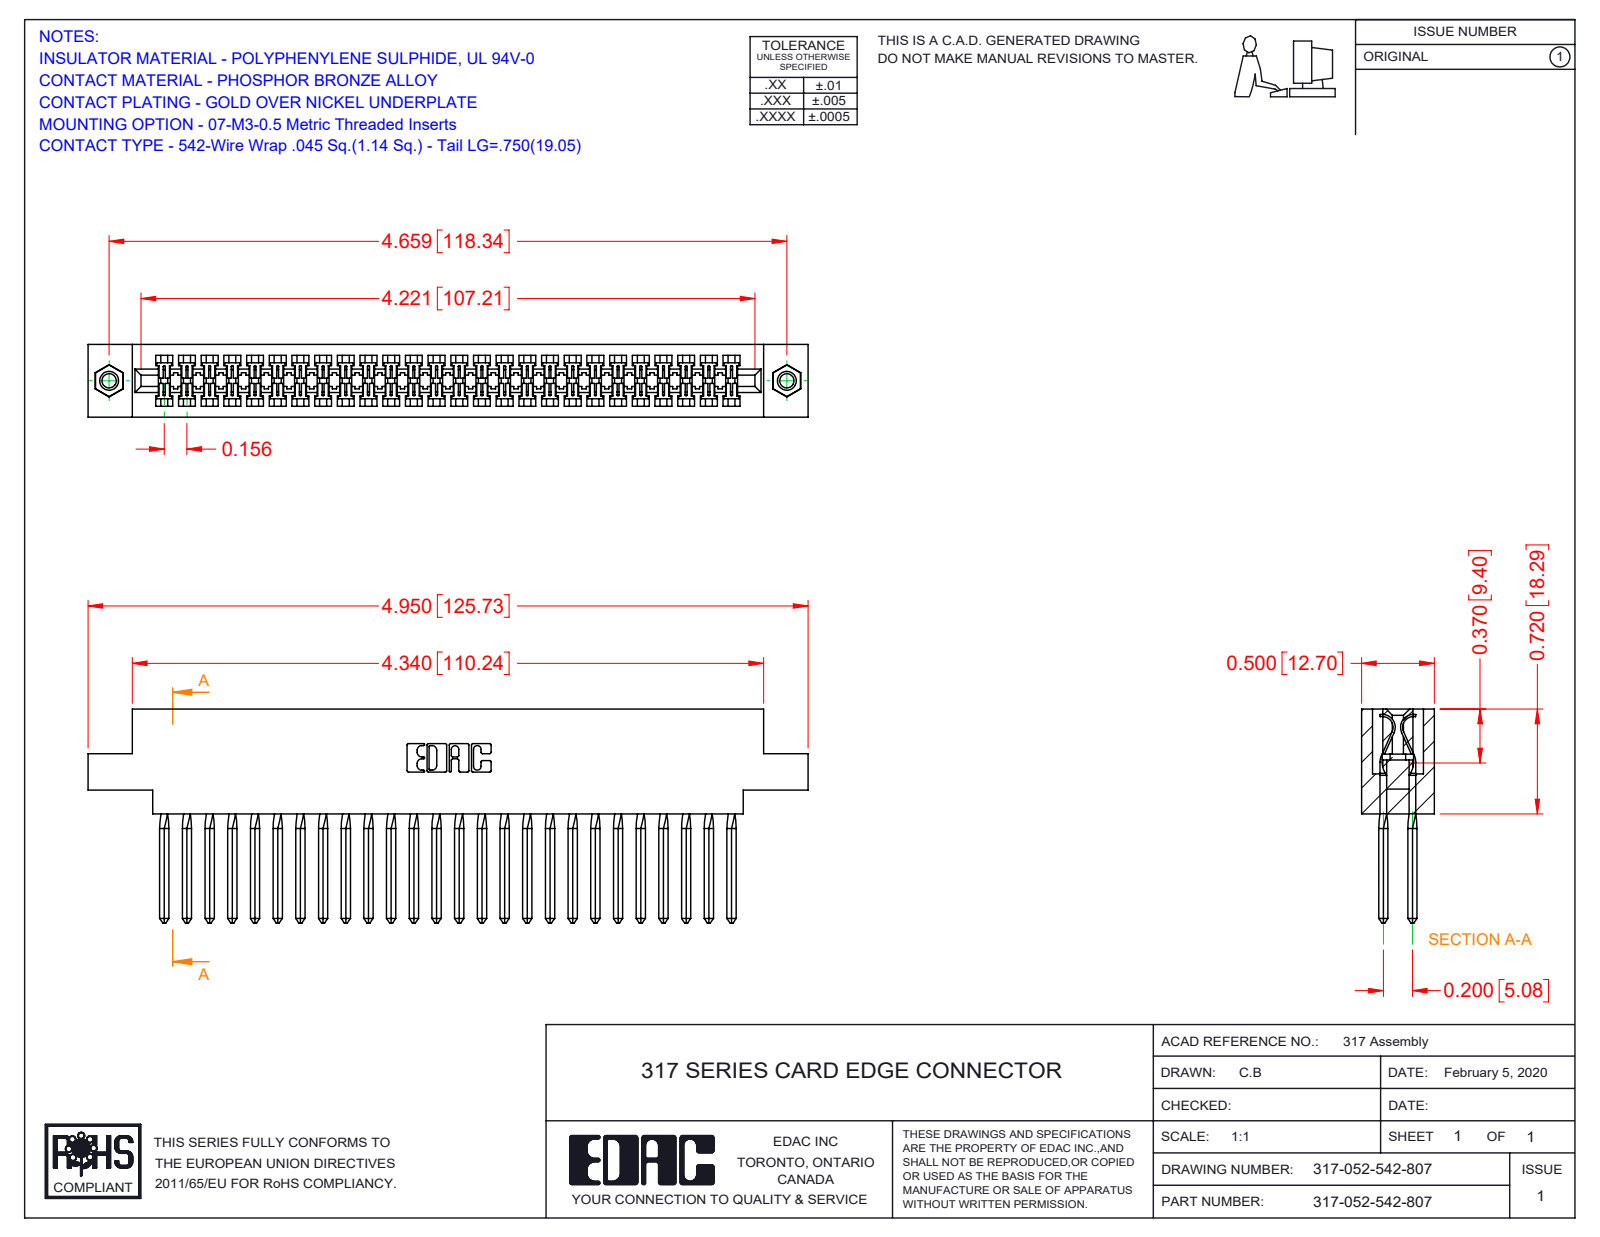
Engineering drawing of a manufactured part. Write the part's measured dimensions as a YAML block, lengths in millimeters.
part_name: "317 Part_.156 Dia - TI; 317-290-003_542; 317-052-542-807; 345-250-001_345-250-005-103"
step_written_by: "SolidWorks 2016 (CONFIG_CONTROL_DESIGN)"
units: millimeters
bodies: {solids: 55, faces: 3126, planar: 2482, cylindrical: 420, other: 224}
overall_size: [125.7, 37.3, 12.7]
volume: 20070
surface_area: 27430
round_holes:
  - {diameter: 2.5, count: 2}
  - {diameter: 3.2, count: 2}
  - {diameter: 4, count: 2}
round_bosses_or_shafts:
  - {diameter: 3.9, count: 2}
partial_cylinders:
  - {radius: 0.2, count: 104}
  - {radius: 0.3, count: 22}
  - {radius: 0.2, count: 6}
  - {radius: 0.8, count: 6}
  - {radius: 0.7, count: 3}
  - {radius: 1.9, count: 2}
  - {radius: 2.3, count: 2}
  - {radius: 2.5, count: 2}
face_to_face_distances: [12.7, 1.9, 10.8, 8.9, 5.1, 2.8, 2.9, 3.5, 1.2, 18.3]
hole_center_spacings: [118.3]
